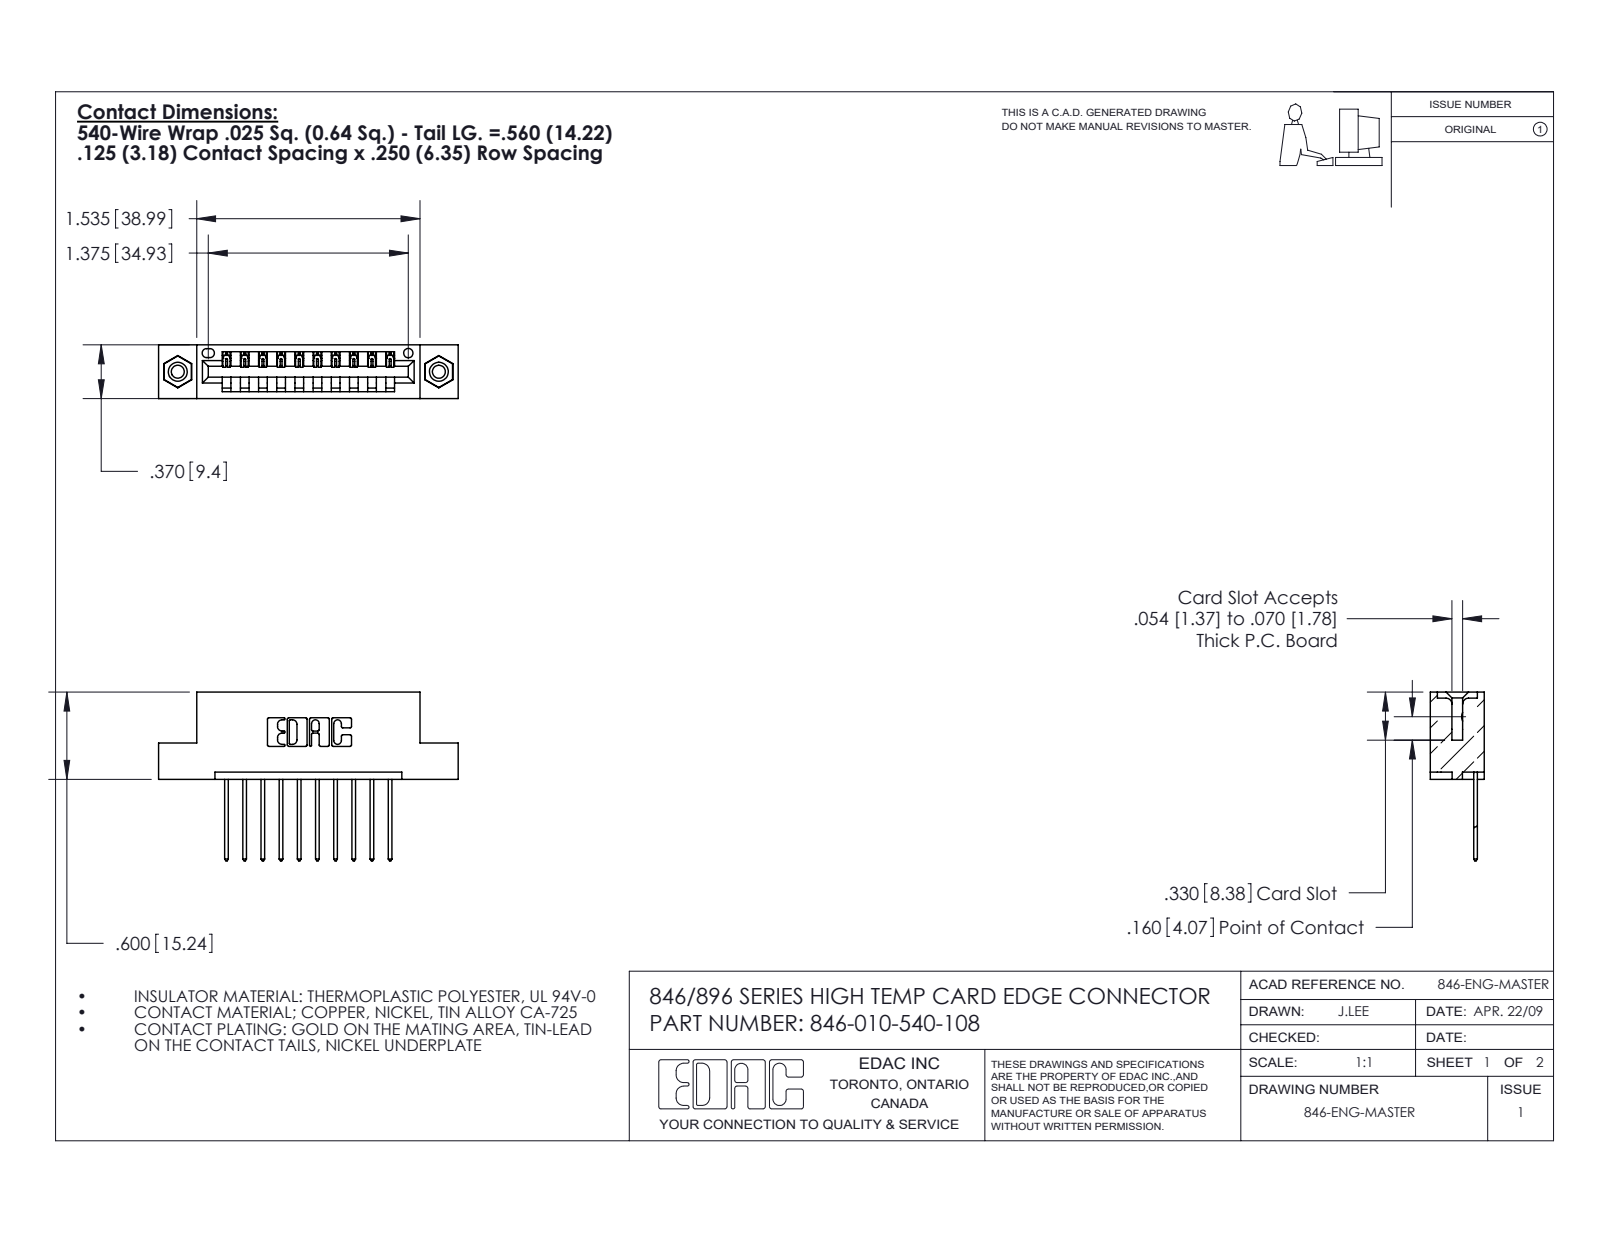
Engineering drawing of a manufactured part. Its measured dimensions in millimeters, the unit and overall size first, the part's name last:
Units: millimetres
Overall size (bounding box): 52.3 × 29.5 × 9.4
Round holes (diameter × count): ⌀2.3 ×2, ⌀3.2 ×2, ⌀4 ×2, ⌀1.6 ×1
Round bosses / shafts (diameter × count): ⌀3.9 ×2
Partial cylindrical surfaces — rounded edges, fillets, slot ends (radius × count): R0.3 ×22, R0.2 ×20, R0.3 ×20, R0.2 ×6, R0.8 ×6, R0.7 ×3, R0.8 ×2, R1 ×2
Main face-to-face distances: 6.4, 1.2, 8.2, 9.4, 1.8, 7.6, 0.6, 3.8, 5.6, 2.5
Hole centre spacings: 6.2, 40.4, 45.6
Volume: 4 800 mm³ · Surface area: 5 768 mm²
Bodies: 13 solids, 762 faces (508 planar, 238 cylindrical, 16 other)
Part name (STEP PRODUCT): 346-010-540-108; 345-250-001_345-250-003-102; 346 Part_Flush Mounting Lugs - 0.156 Dia-TI; 345-292-001_345-293-140
STEP written by: SolidWorks 2016 (CONFIG_CONTROL_DESIGN)
